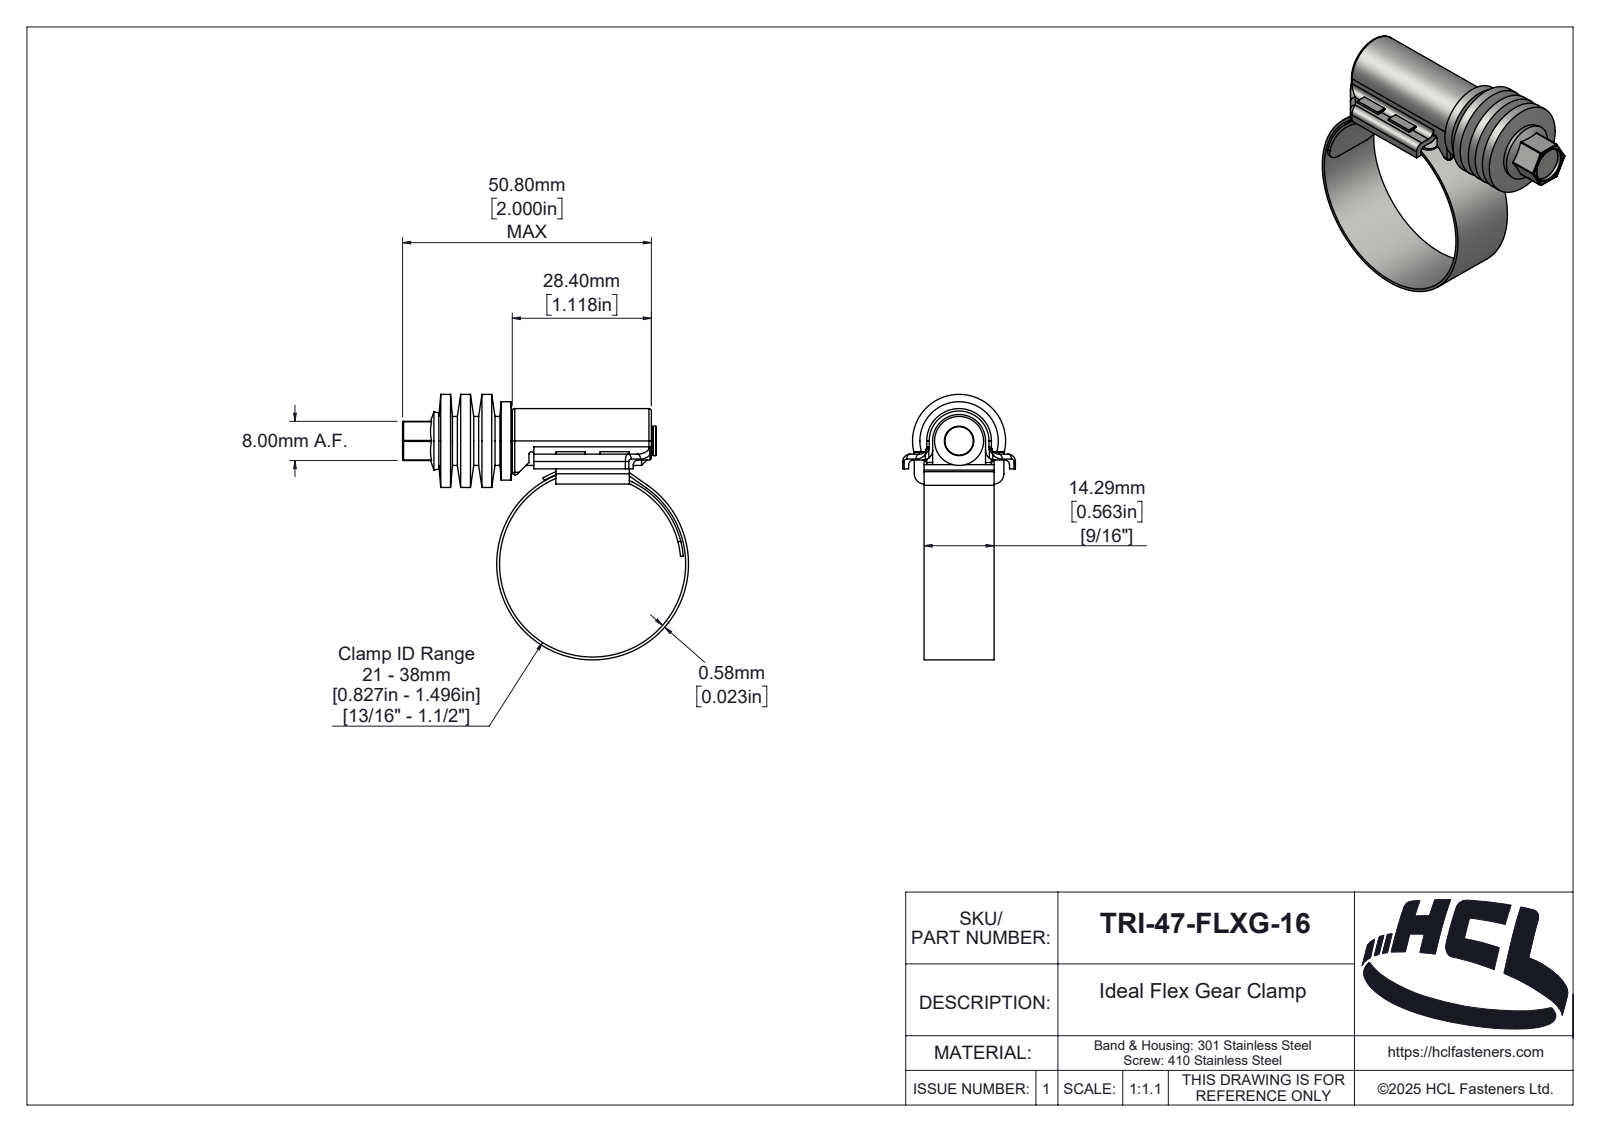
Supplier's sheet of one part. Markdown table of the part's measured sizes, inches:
| quantity | value |
| --- | --- |
| part name | TRI-47-FLXG-16 |
| STEP written by | SolidWorks 2025 (AUTOMOTIVE_DESIGN) |
| units | inches |
| bodies | 4 solids, 323 faces (88 planar, 139 cylindrical, 96 other) |
| overall size | 2.298 × 2.133 × 0.906 |
| volume | 0.543 in³ |
| surface area | 17.34 in² |
| round holes (diameter × count) | 0.276 × 1, 1.496 × 1 |
| round bosses / shafts (diameter × count) | 1.542 × 1, 0.748 × 1, 0.63 × 1, 0.394 × 1, 0.236 × 1, 0.197 × 1 |
| partial cylindrical surfaces (radius × count) | 0.008 × 12, 0.02 × 9, 0.039 × 8, 0.059 × 4, 0.118 × 4, 0.079 × 3, 0.004 × 2, 0.083 × 2 |
| main face-to-face distances | 0.079, 0.047, 0.193, 0.069, 0.494, 0.641, 0.24, 0.562, 0.021, 0.541 |
